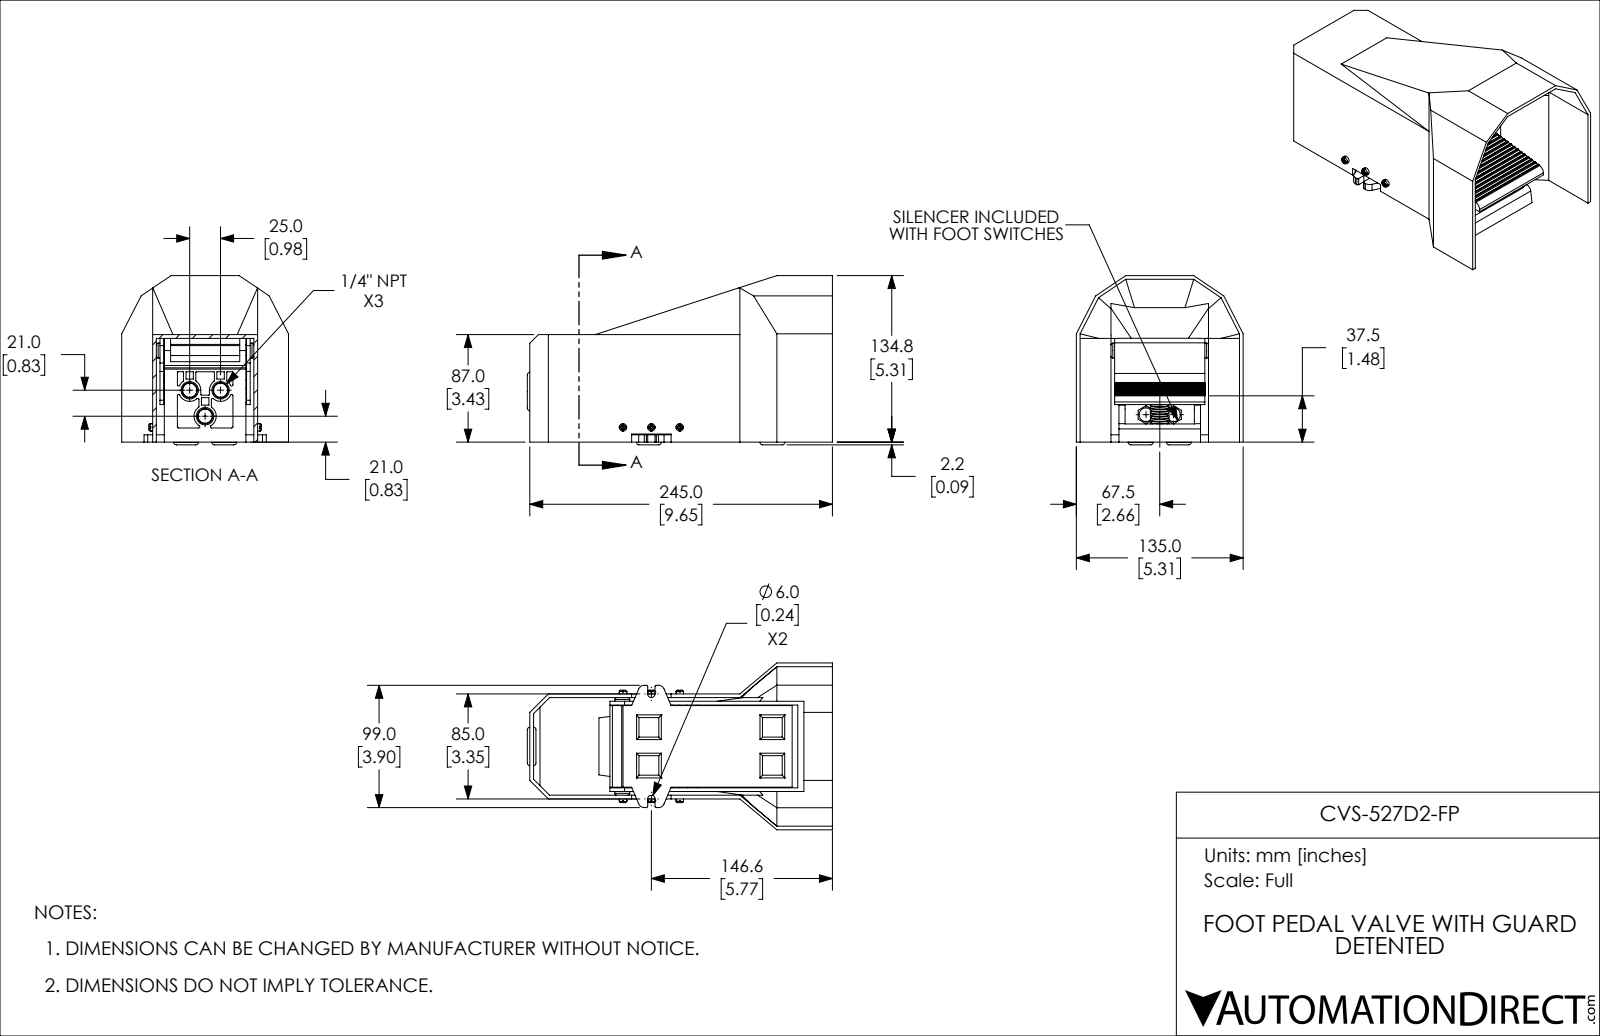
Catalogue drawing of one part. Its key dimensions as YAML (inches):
part_name: "CVS-527D2-FP"
step_written_by: "SolidWorks 2021 (CONFIG_CONTROL_DESIGN)"
units: inches
bodies: {solids: 5, faces: 641, planar: 358, cylindrical: 173, other: 110}
overall_size: [9.724, 5.394, 5.315]
volume: 39.07
surface_area: 405.8
round_holes:
  - {diameter: 0.63, count: 2}
  - {diameter: 0.394, count: 1}
  - {diameter: 0.472, count: 1}
  - {diameter: 0.787, count: 1}
round_bosses_or_shafts:
  - {diameter: 0.512, count: 4}
  - {diameter: 0.236, count: 3}
  - {diameter: 0.787, count: 2}
  - {diameter: 0.437, count: 2}
  - {diameter: 0.472, count: 1}
  - {diameter: 0.315, count: 1}
partial_cylinders:
  - {radius: 0.02, count: 32}
  - {radius: 0.039, count: 15}
  - {radius: 0.197, count: 11}
  - {radius: 0.079, count: 7}
  - {radius: 0.394, count: 4}
  - {radius: 0.118, count: 3}
  - {radius: 0.354, count: 3}
  - {radius: 0.087, count: 2}
face_to_face_distances: [0.118, 3.228, 3.11, 0.197, 0.984, 4.213, 1.102, 4.094, 0.236, 3.976]
